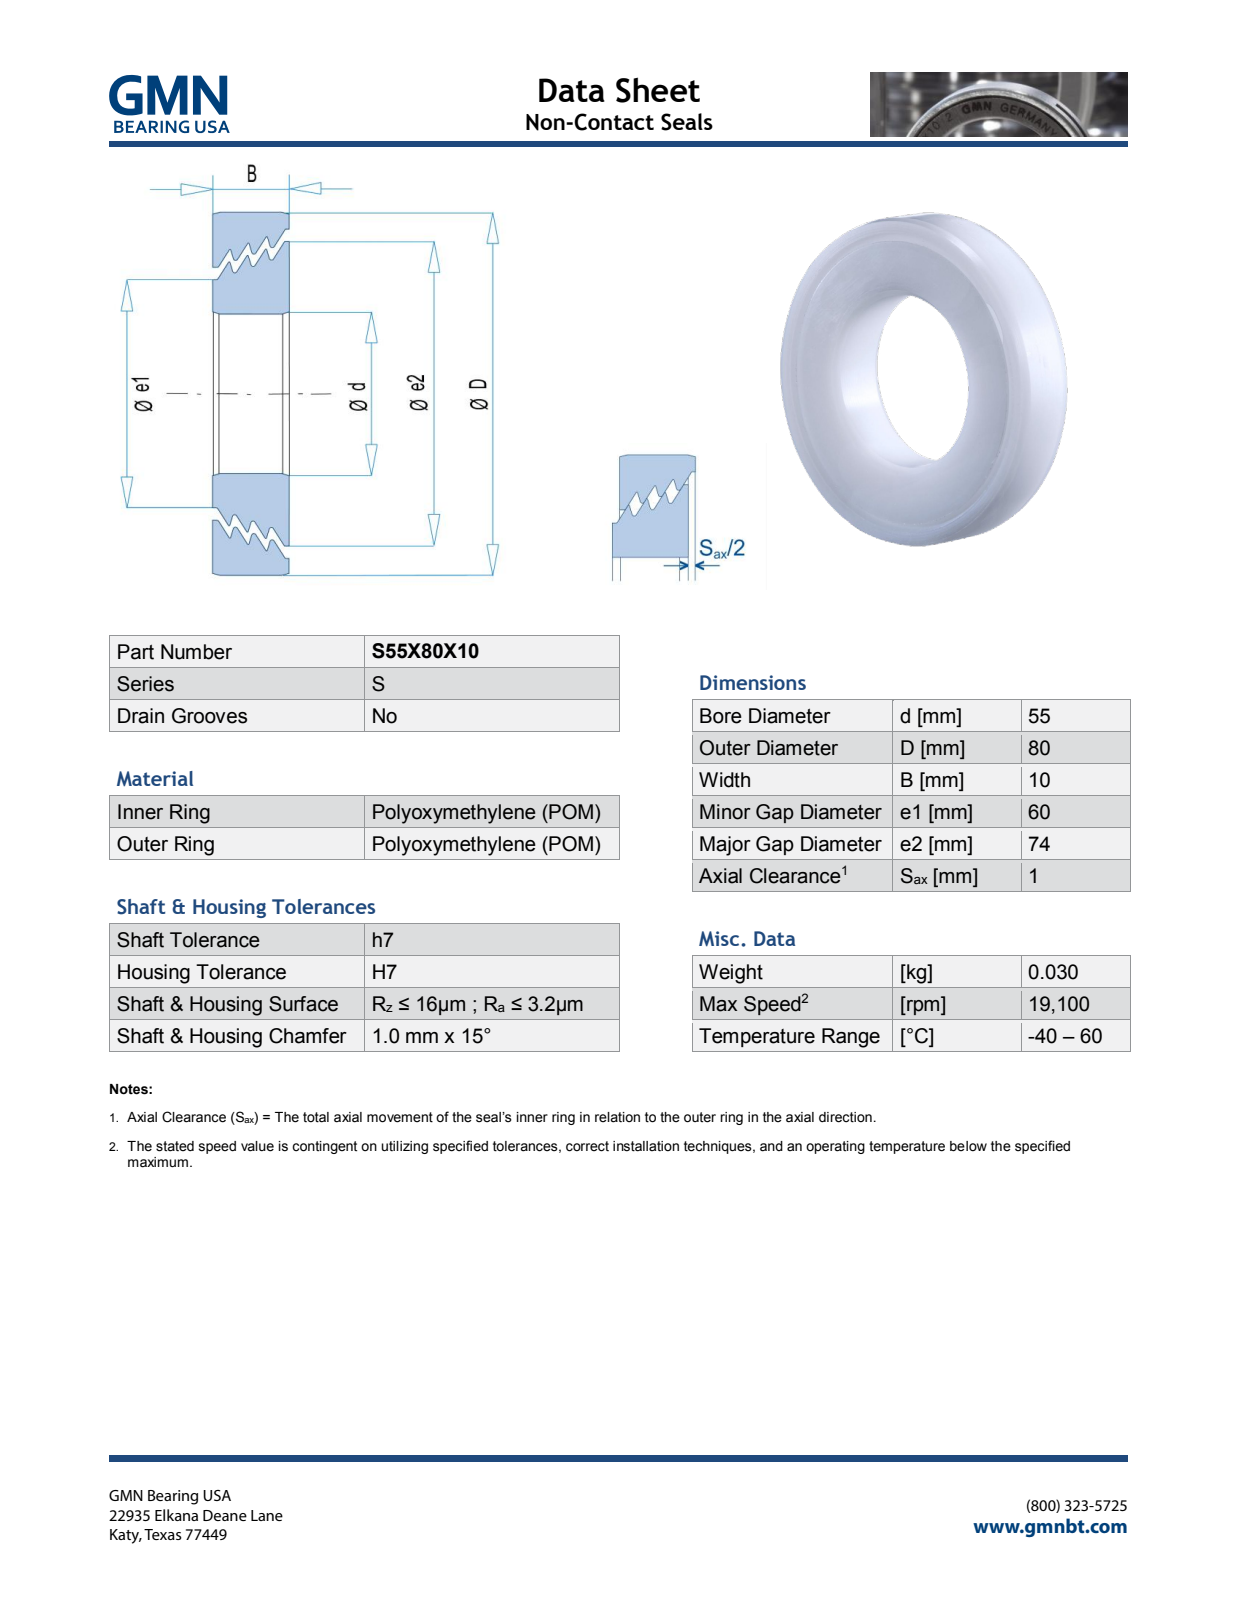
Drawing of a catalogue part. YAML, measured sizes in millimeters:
part_name: "S55X80X10_PRT"
step_written_by: "PRO/ENGINEER BY PARAMETRIC TECHNOLOGY CORPORATION, 2013150 (AUTOMOTIVE_DESIGN)"
units: millimeters
bodies: {solids: 2, faces: 690, planar: 610, cylindrical: 12, other: 68}
overall_size: [80, 80, 10.07]
volume: 24658
surface_area: 17524
round_holes:
  - {diameter: 55, count: 1}
  - {diameter: 61.63, count: 1}
  - {diameter: 75.63, count: 1}
round_bosses_or_shafts:
  - {diameter: 80, count: 1}
  - {diameter: 74, count: 1}
  - {diameter: 60, count: 1}
face_to_face_distances: [10, 10.07, 0.33, 0.32, 2.58, 2.26, 1.83, 2.59, 1.93, 2.25]
